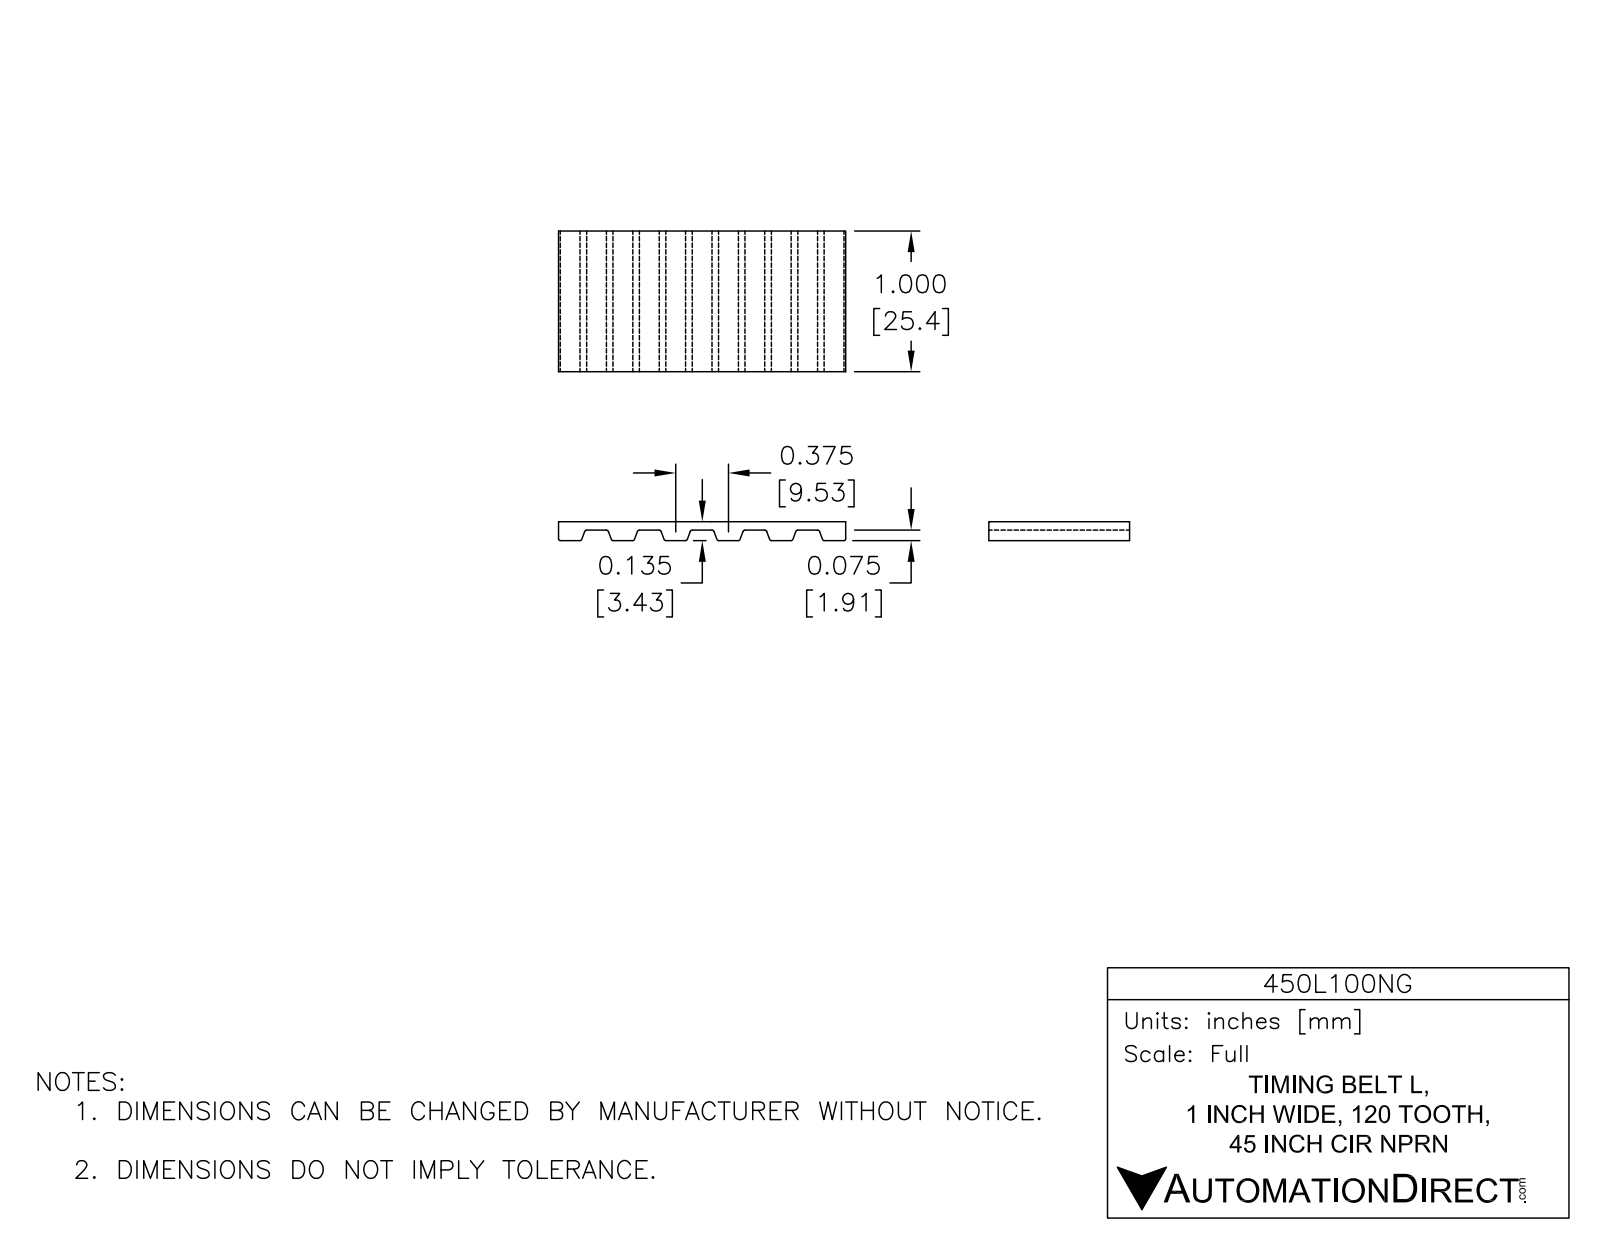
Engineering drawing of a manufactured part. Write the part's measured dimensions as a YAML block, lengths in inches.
part_name: "450L100NG"
step_written_by: "SolidWorks 2014 (AUTOMOTIVE_DESIGN)"
units: inches
bodies: {solids: 1, faces: 976, planar: 457, cylindrical: 519, other: 0}
overall_size: [20.788, 3, 1]
volume: 4.083
surface_area: 108.5
partial_cylinders:
  - {radius: 0.02, count: 476}
  - {radius: 1.435, count: 2}
  - {radius: 1.5, count: 2}
face_to_face_distances: [0.065, 2.935, 3, 2.87, 0.14, 2.86, 0.075, 2.795, 1, 2.72]
